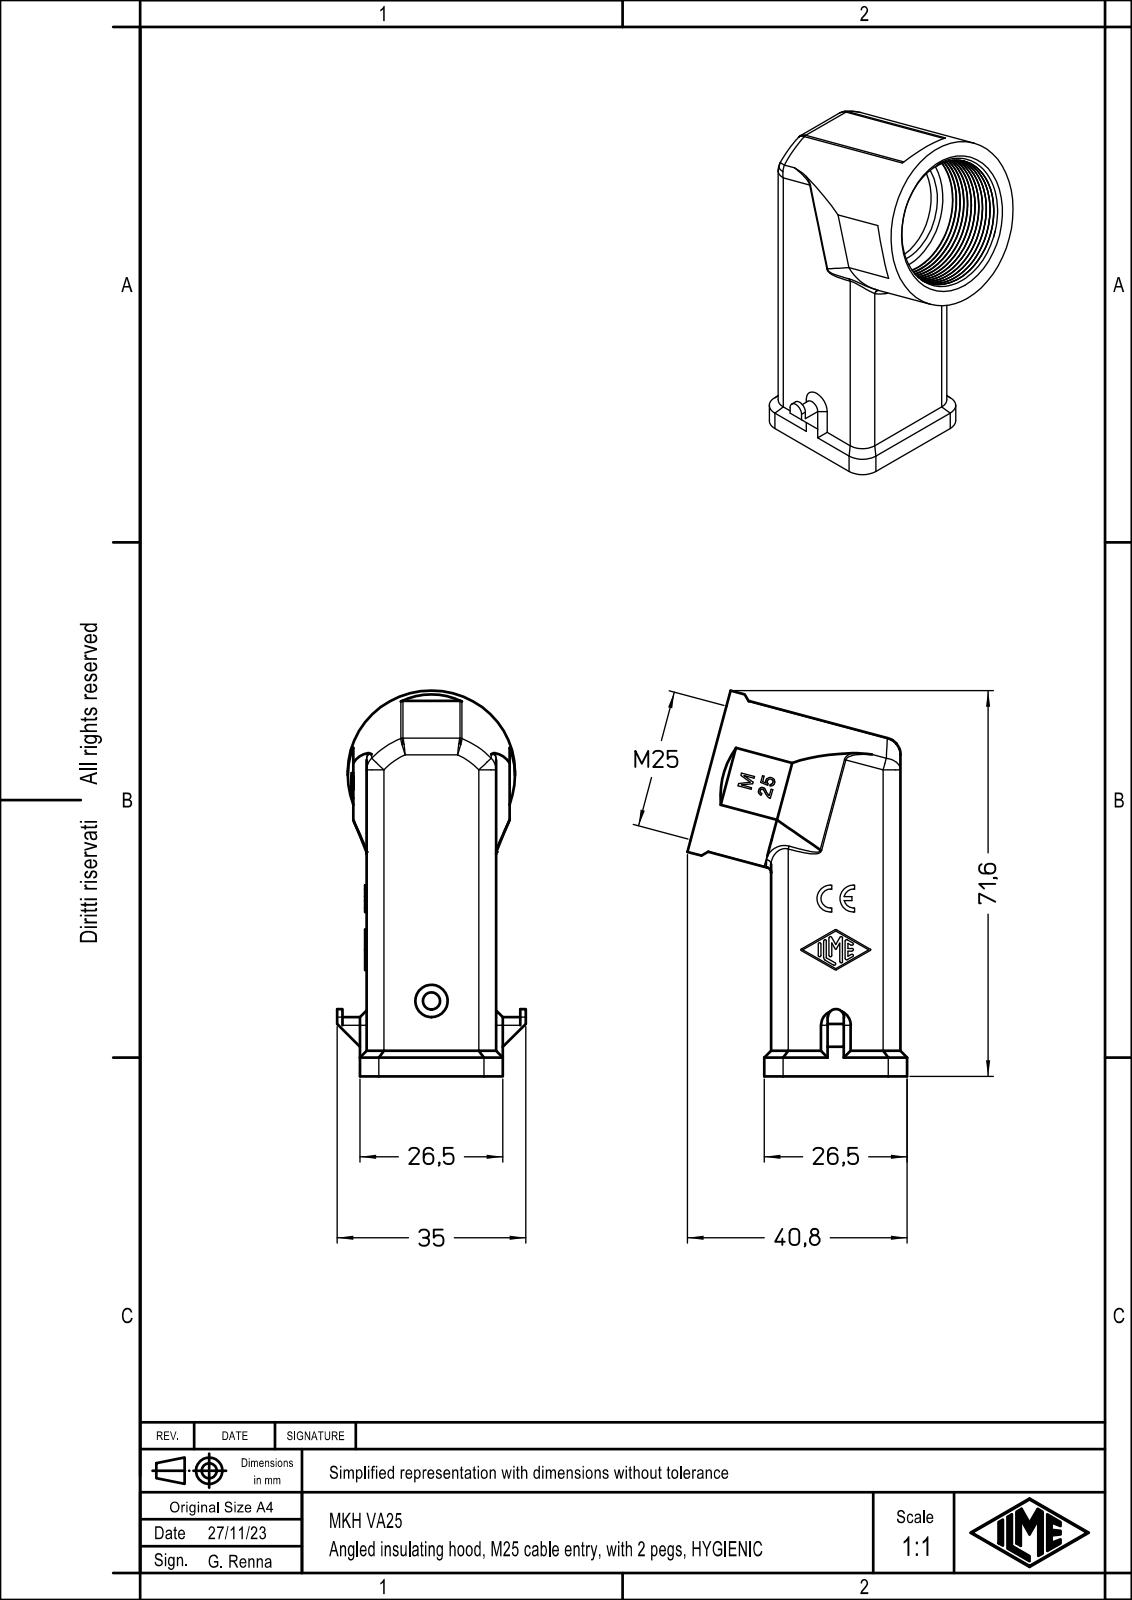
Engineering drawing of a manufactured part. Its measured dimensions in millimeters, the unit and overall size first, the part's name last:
Units: millimetres
Overall size (bounding box): 71.62 × 40.76 × 35
Round holes (diameter × count): ⌀3.2 ×1, ⌀20.6 ×1, ⌀23.6 ×1
Round bosses / shafts (diameter × count): ⌀31 ×1
Partial cylindrical surfaces — rounded edges, fillets, slot ends (radius × count): R0.25 ×15, R2 ×13, R3.2 ×7, R1 ×4, R3.5 ×4, R0.12 ×3, R1.5 ×2, R1.75 ×2
Main face-to-face distances: 24, 1.25, 26.5, 25.25, 1.1, 25.4, 24.15, 1.83, 2.5, 29
Volume: 13 177 mm³ · Surface area: 14 092 mm²
Bodies: 1 solid, 336 faces (222 planar, 67 cylindrical, 47 other)
Part name (STEP PRODUCT): MKH VA25
STEP written by: Creo Elements/Direct Modeling 20.1B 02-Apr-2019 (C) Parametric Technology GmbH (AUTOMOTIVE_DESIGN)
